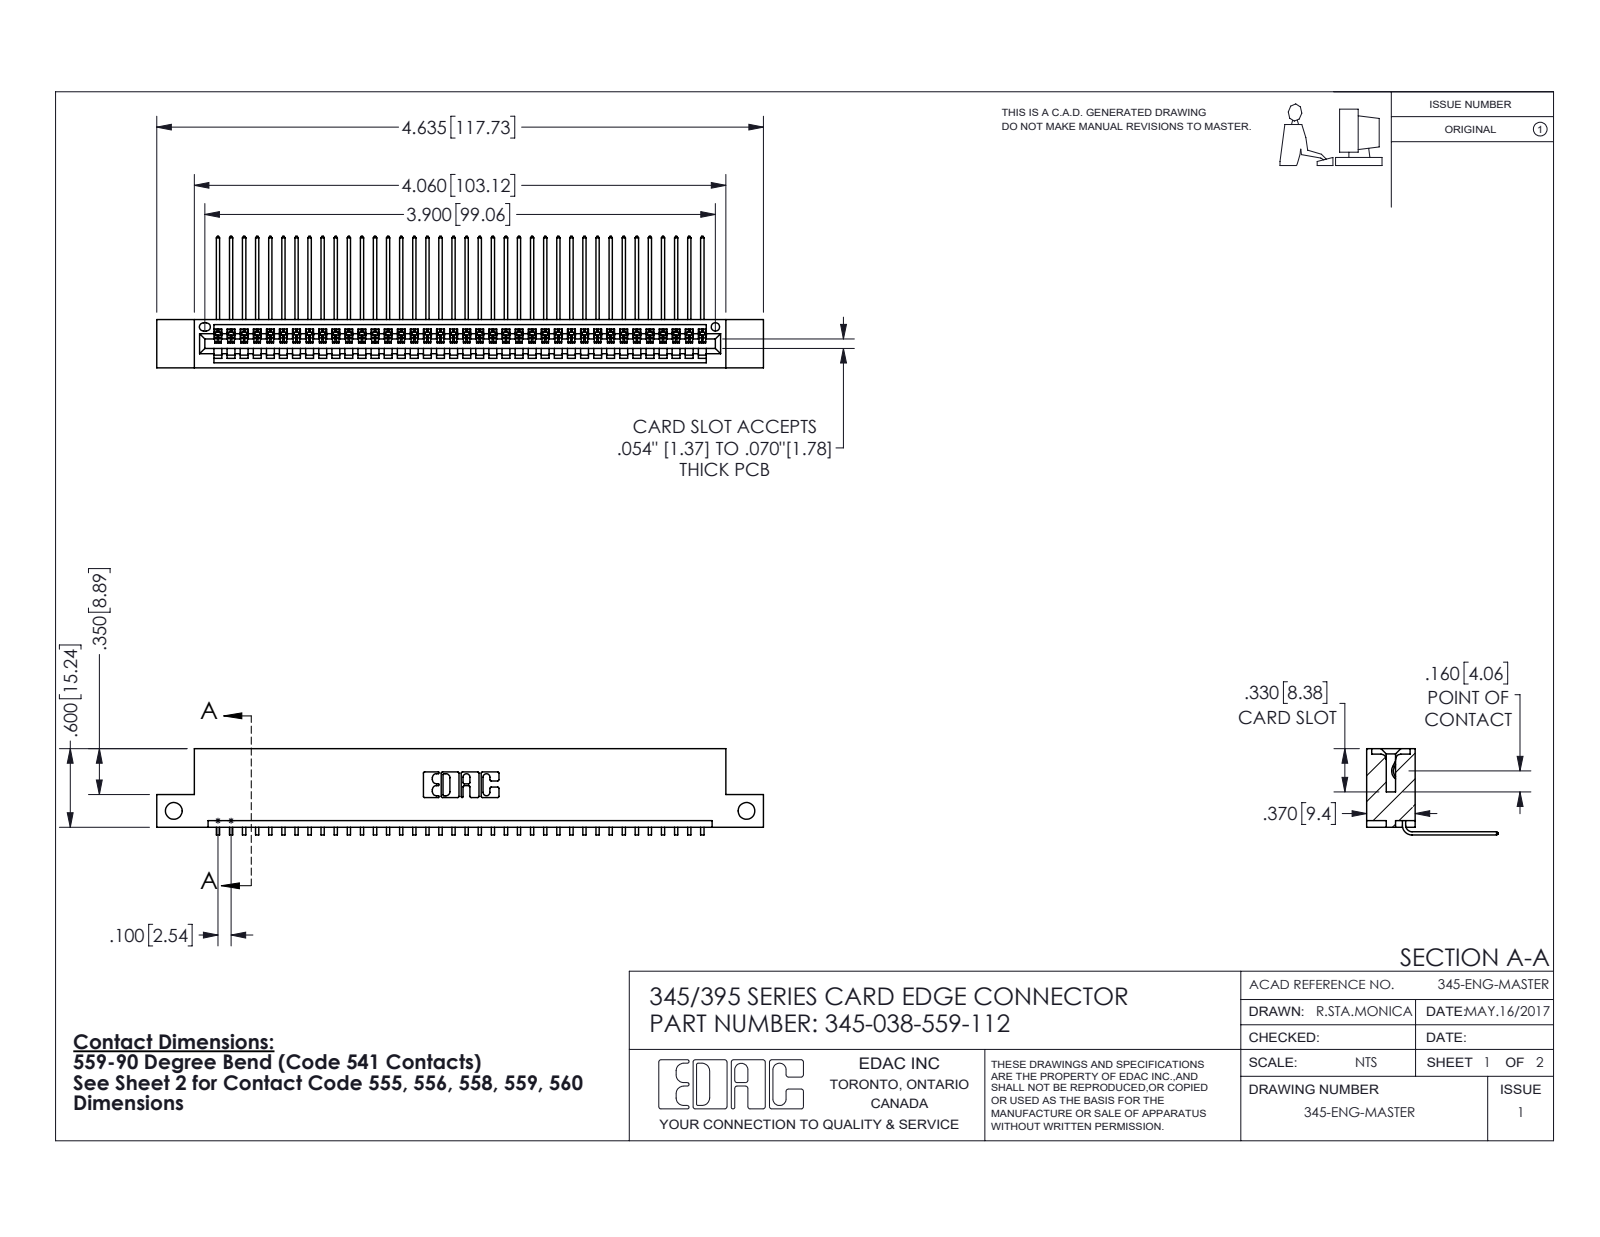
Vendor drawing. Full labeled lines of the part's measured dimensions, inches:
Part name (STEP PRODUCT): 345-038-559-112; 345 Part_Flush Mounting Lugs - Side Mount; 345-292-001_558 559 Tail - 1
STEP written by: SolidWorks 2016 (CONFIG_CONTROL_DESIGN)
Units: inches
Bodies: 39 solids, 2406 faces (1676 planar, 730 cylindrical, 0 other)
Overall size (bounding box): 4.635 × 1.005 × 0.659
Volume: 0.683 in³ · Surface area: 23.9 in²
Round holes (diameter × count): ⌀0.128 ×2, ⌀0.064 ×1
Partial cylindrical surfaces — rounded edges, fillets, slot ends (radius × count): R0.006 ×76, R0.01 ×22, R0.007 ×6, R0.031 ×6, R0.026 ×3, R0.031 ×2, R0.04 ×2, R0.014 ×1
Main face-to-face distances: 0.298, 0.072, 0.37, 0.2, 0.098, 0.272, 0.025, 0.225, 0.149, 0.072
Hole centre spacings: 4.375
